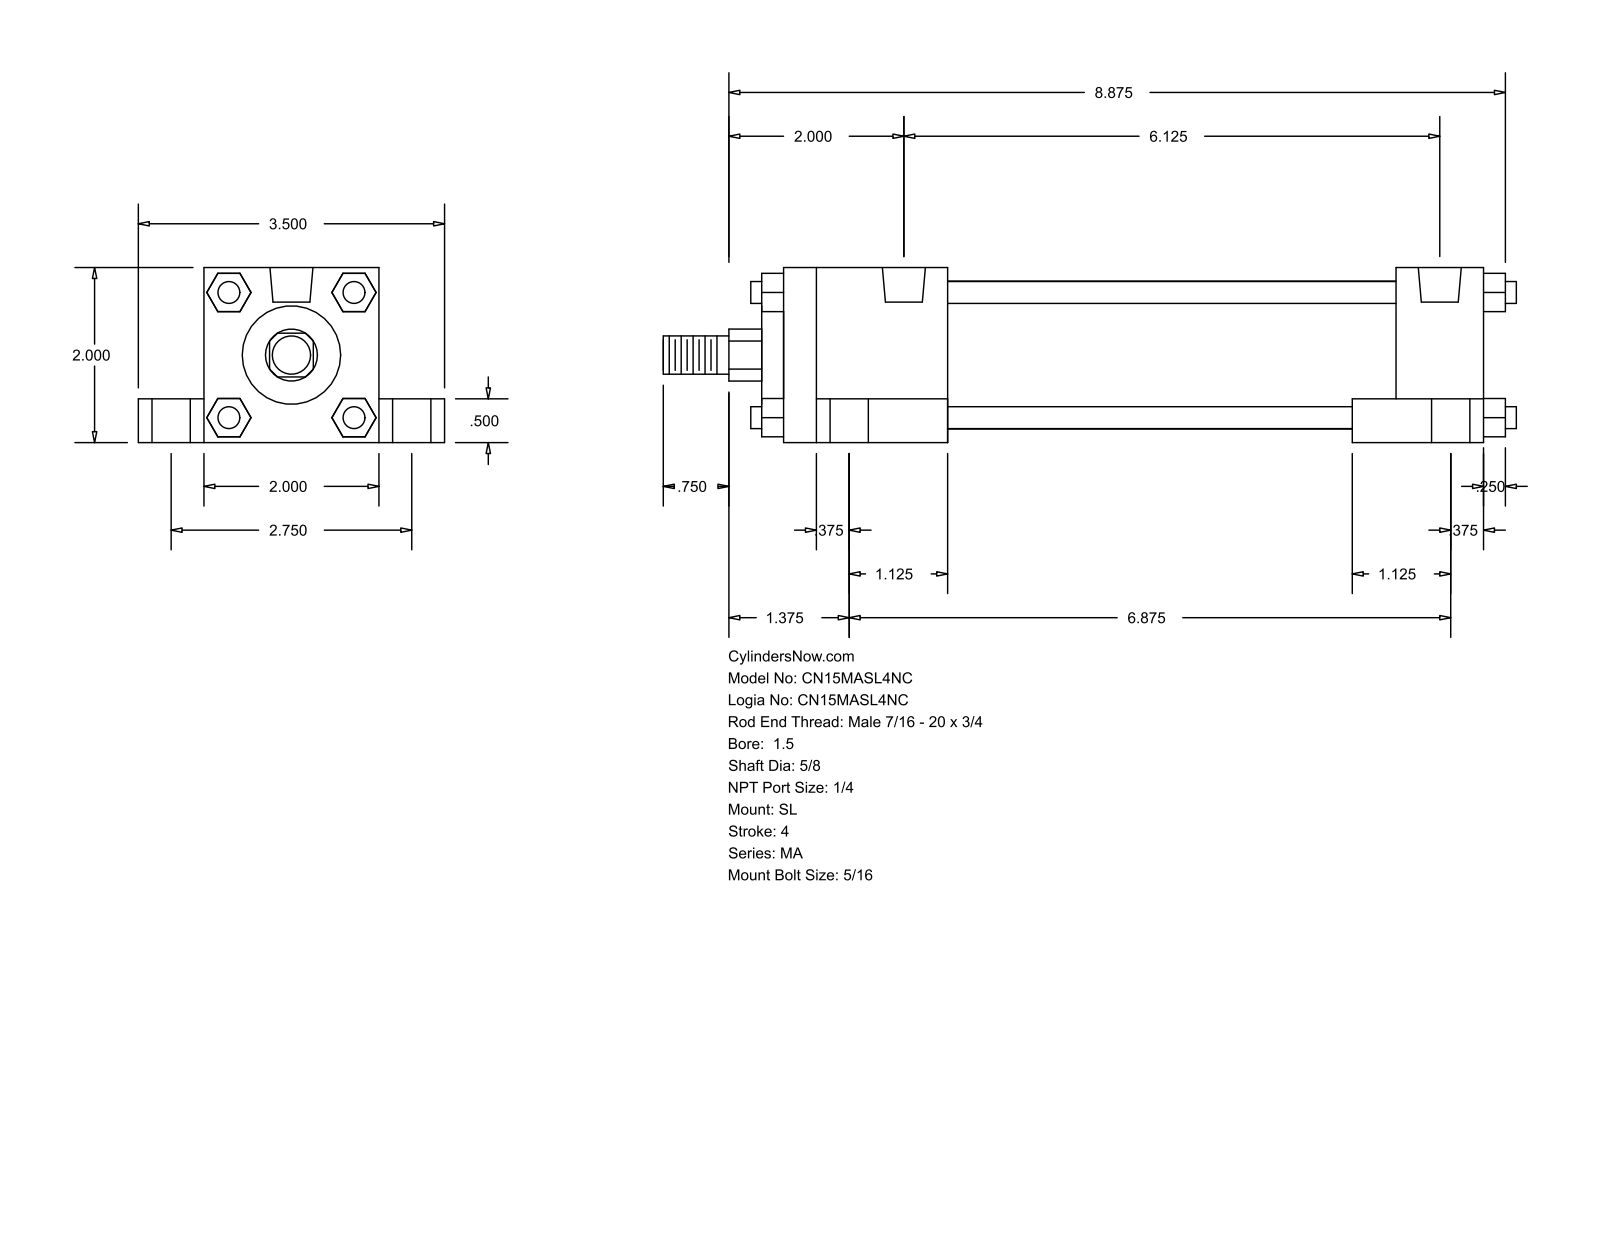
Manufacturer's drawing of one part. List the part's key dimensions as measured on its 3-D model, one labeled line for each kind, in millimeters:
Part name (STEP PRODUCT): MA_SL__0150_0.625
STEP written by: GSSL Pune (CONFIG_CONTROL_DESIGN)
Units: millimetres
Bodies: 0 solids, 148 faces (112 planar, 36 cylindrical, 0 other)
Overall size (bounding box): 247.65 × 88.9 × 50.8
Round holes (diameter × count): ⌀7.94 ×4, ⌀11.11 ×4, ⌀17.46 ×4, ⌀12.49 ×2
Round bosses / shafts (diameter × count): ⌀6.35 ×4, ⌀42.93 ×1, ⌀28.57 ×1, ⌀15.88 ×1, ⌀11.11 ×1
Partial cylindrical surfaces — rounded edges, fillets, slot ends (radius × count): R7.54 ×1
Main face-to-face distances: 50.8, 19.05, 38.1, 69.85, 12.7, 203.19, 9.52, 177.8, 25.39, 47.62
Hole centre spacings: 35.06, 38.36, 69.84, 155.58, 162.55, 174.63, 174.98, 188.08
